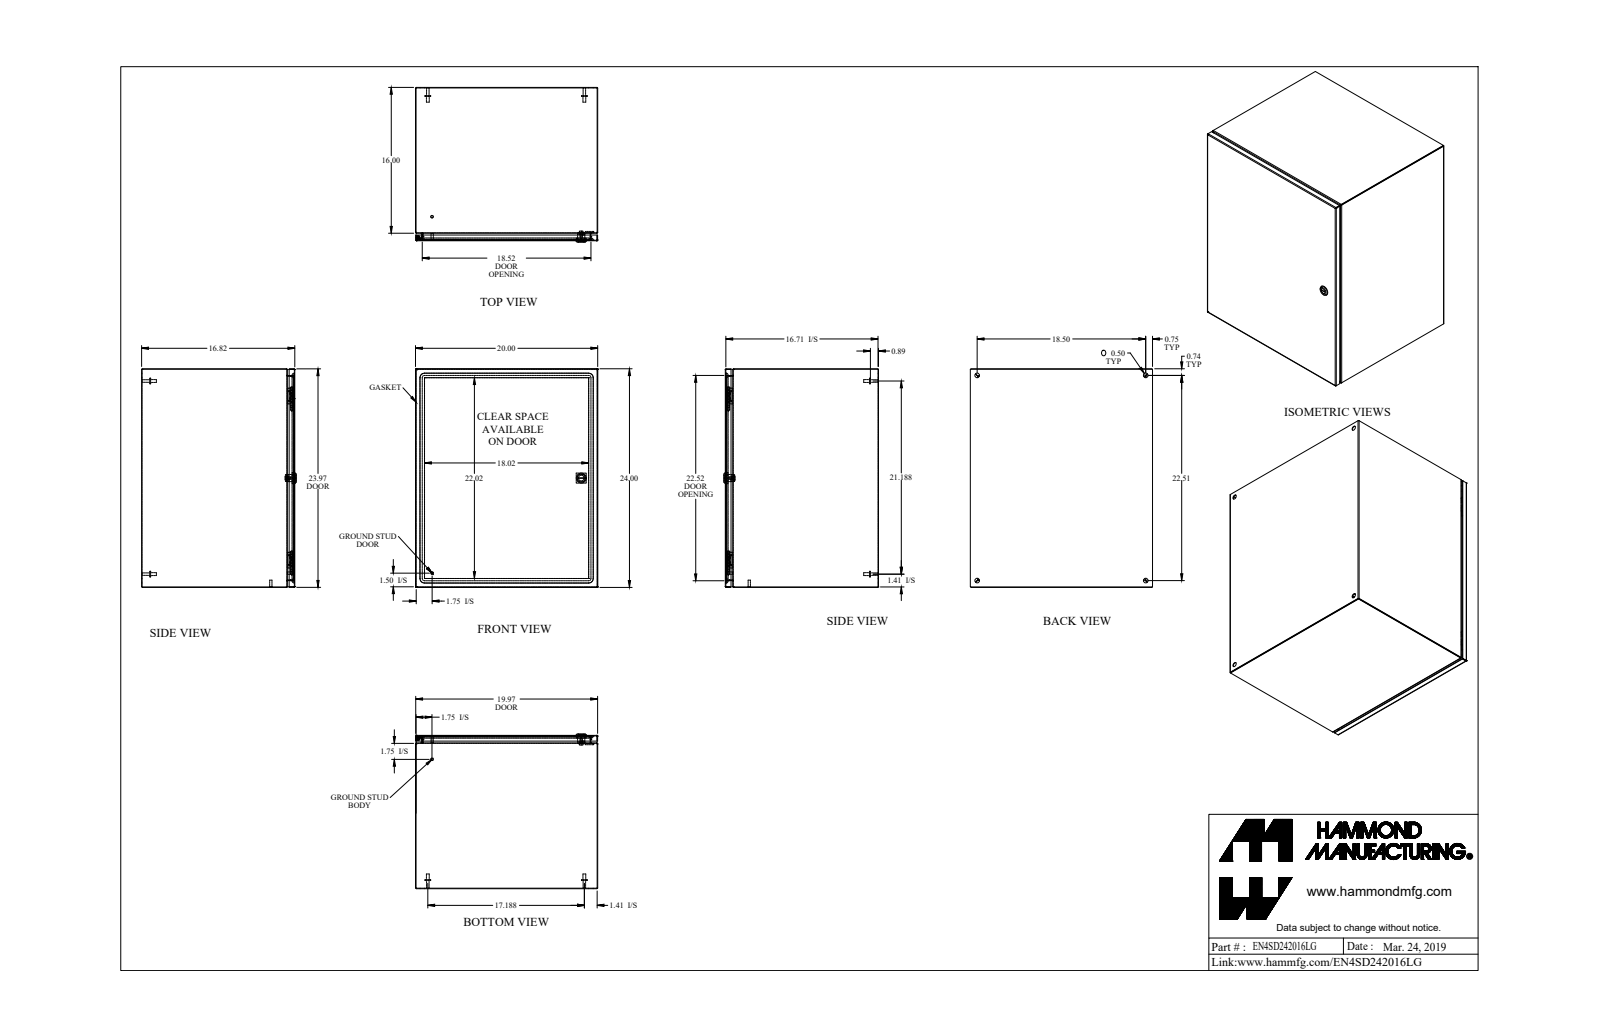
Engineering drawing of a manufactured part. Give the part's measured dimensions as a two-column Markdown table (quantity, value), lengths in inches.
| quantity | value |
| --- | --- |
| part name | EN4SD242016LG |
| STEP written by | SolidWorks 2019 (AUTOMOTIVE_DESIGN) |
| units | inches |
| bodies | 23 solids, 591 faces (266 planar, 201 cylindrical, 124 other) |
| overall size | 24 × 20 × 16.982 |
| volume | 160.8 in³ |
| surface area | 5 270 in² |
| round holes (diameter × count) | 0.5 × 4, 0.172 × 1, 0.232 × 1, 0.24 × 1, 0.242 × 1, 0.625 × 1, 0.785 × 1 |
| round bosses / shafts (diameter × count) | 0.625 × 4, 0.313 × 4, 0.27 × 4, 0.281 × 2, 0.25 × 2, 1.1 × 1, 0.525 × 1, 0.455 × 1 |
| partial cylindrical surfaces (radius × count) | 0.029 × 15, 0.086 × 15, 0.188 × 12, 0.1 × 8, 0.006 × 4, 0.062 × 4, 0.25 × 4, 0.499 × 4 |
| main face-to-face distances | 0.057, 19.943, 23.943, 0.072, 16.765, 16.693, 16.75, 16.822, 19.886, 20 |
| hole center spacings | 18.5, 22.514, 29.14, 11.299, 11.314, 20.755, 20.763 |
